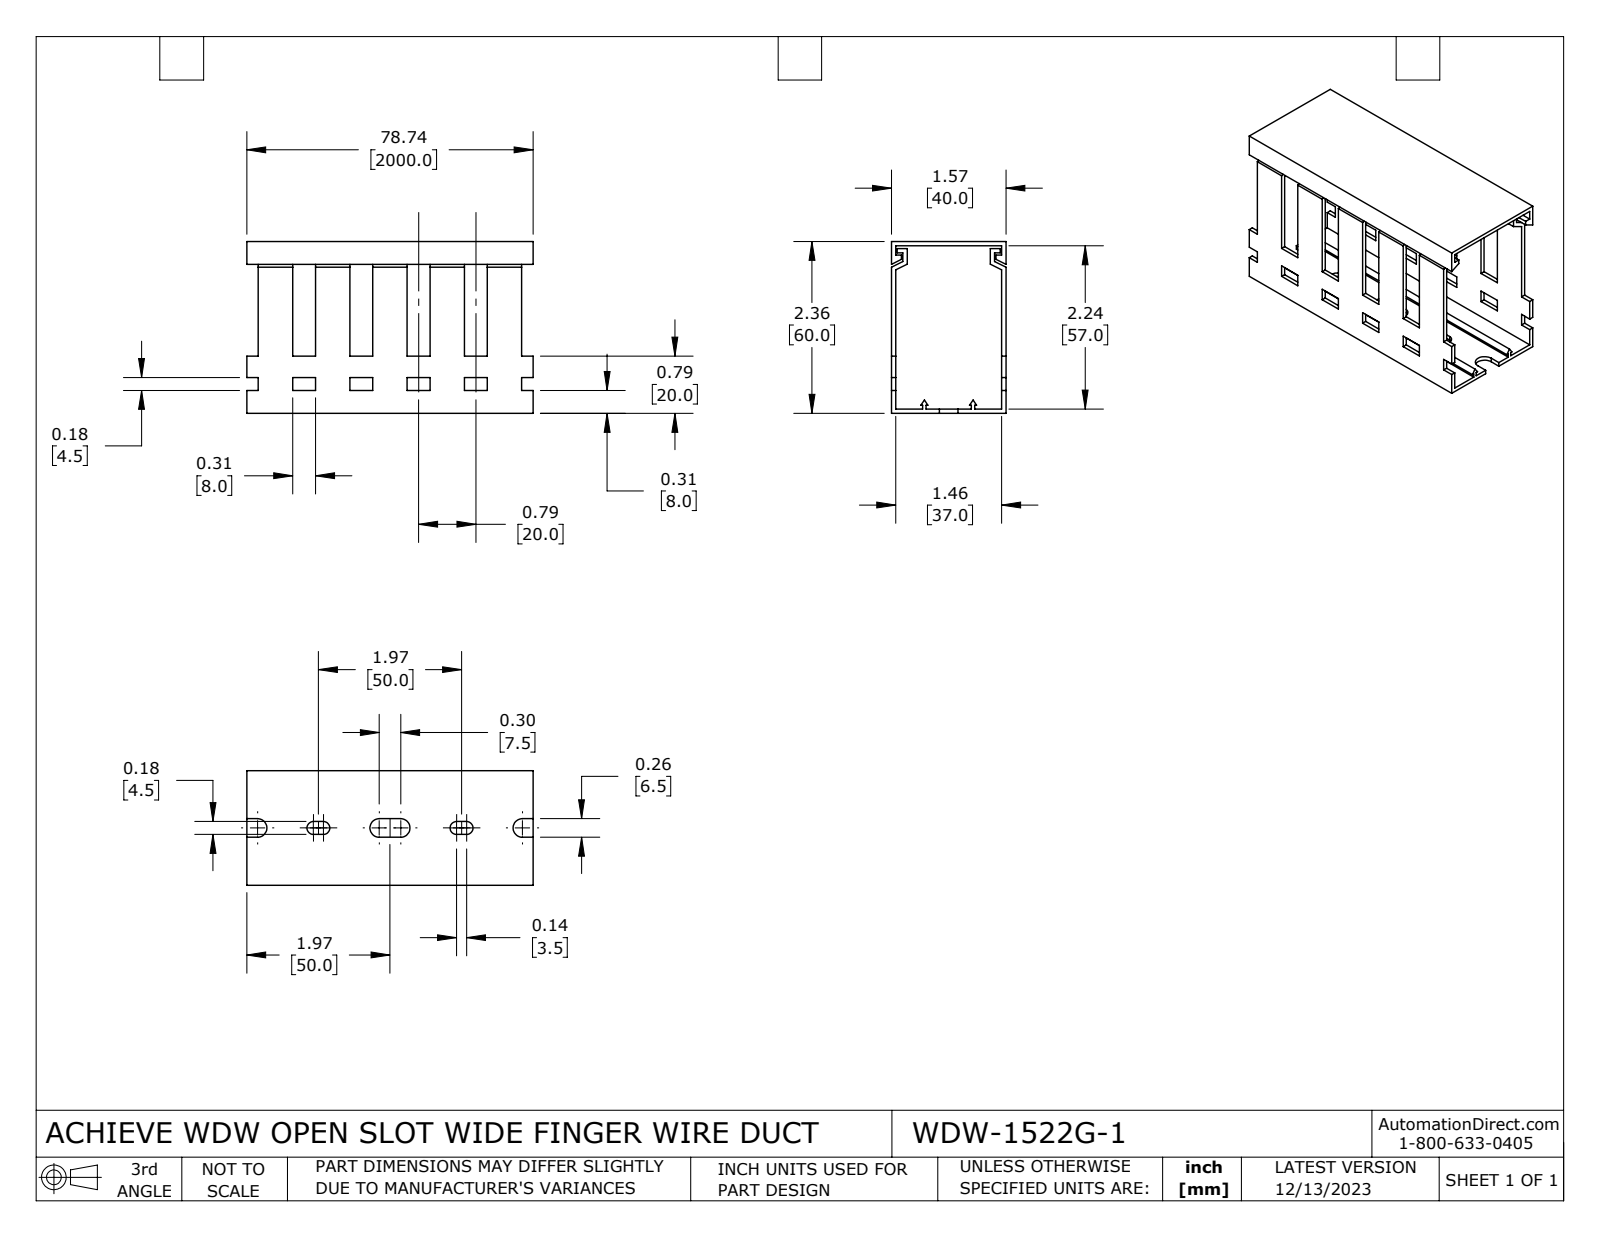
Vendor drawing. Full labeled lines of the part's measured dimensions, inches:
Part name (STEP PRODUCT): WDW-1522G-1
STEP written by: SolidWorks 2023 (CONFIG_CONTROL_DESIGN)
Units: inches
Bodies: 2 solids, 210 faces (198 planar, 12 cylindrical, 0 other)
Overall size (bounding box): 3.937 × 2.362 × 1.575
Volume: 1.686 in³ · Surface area: 61.44 in²
Partial cylindrical surfaces — rounded edges, fillets, slot ends (radius × count): R0.089 ×4, R0.128 ×4
Main face-to-face distances: 0.059, 1.516, 2.303, 1.575, 2.362, 1.457, 2.244, 0.157, 0.787, 1.358
